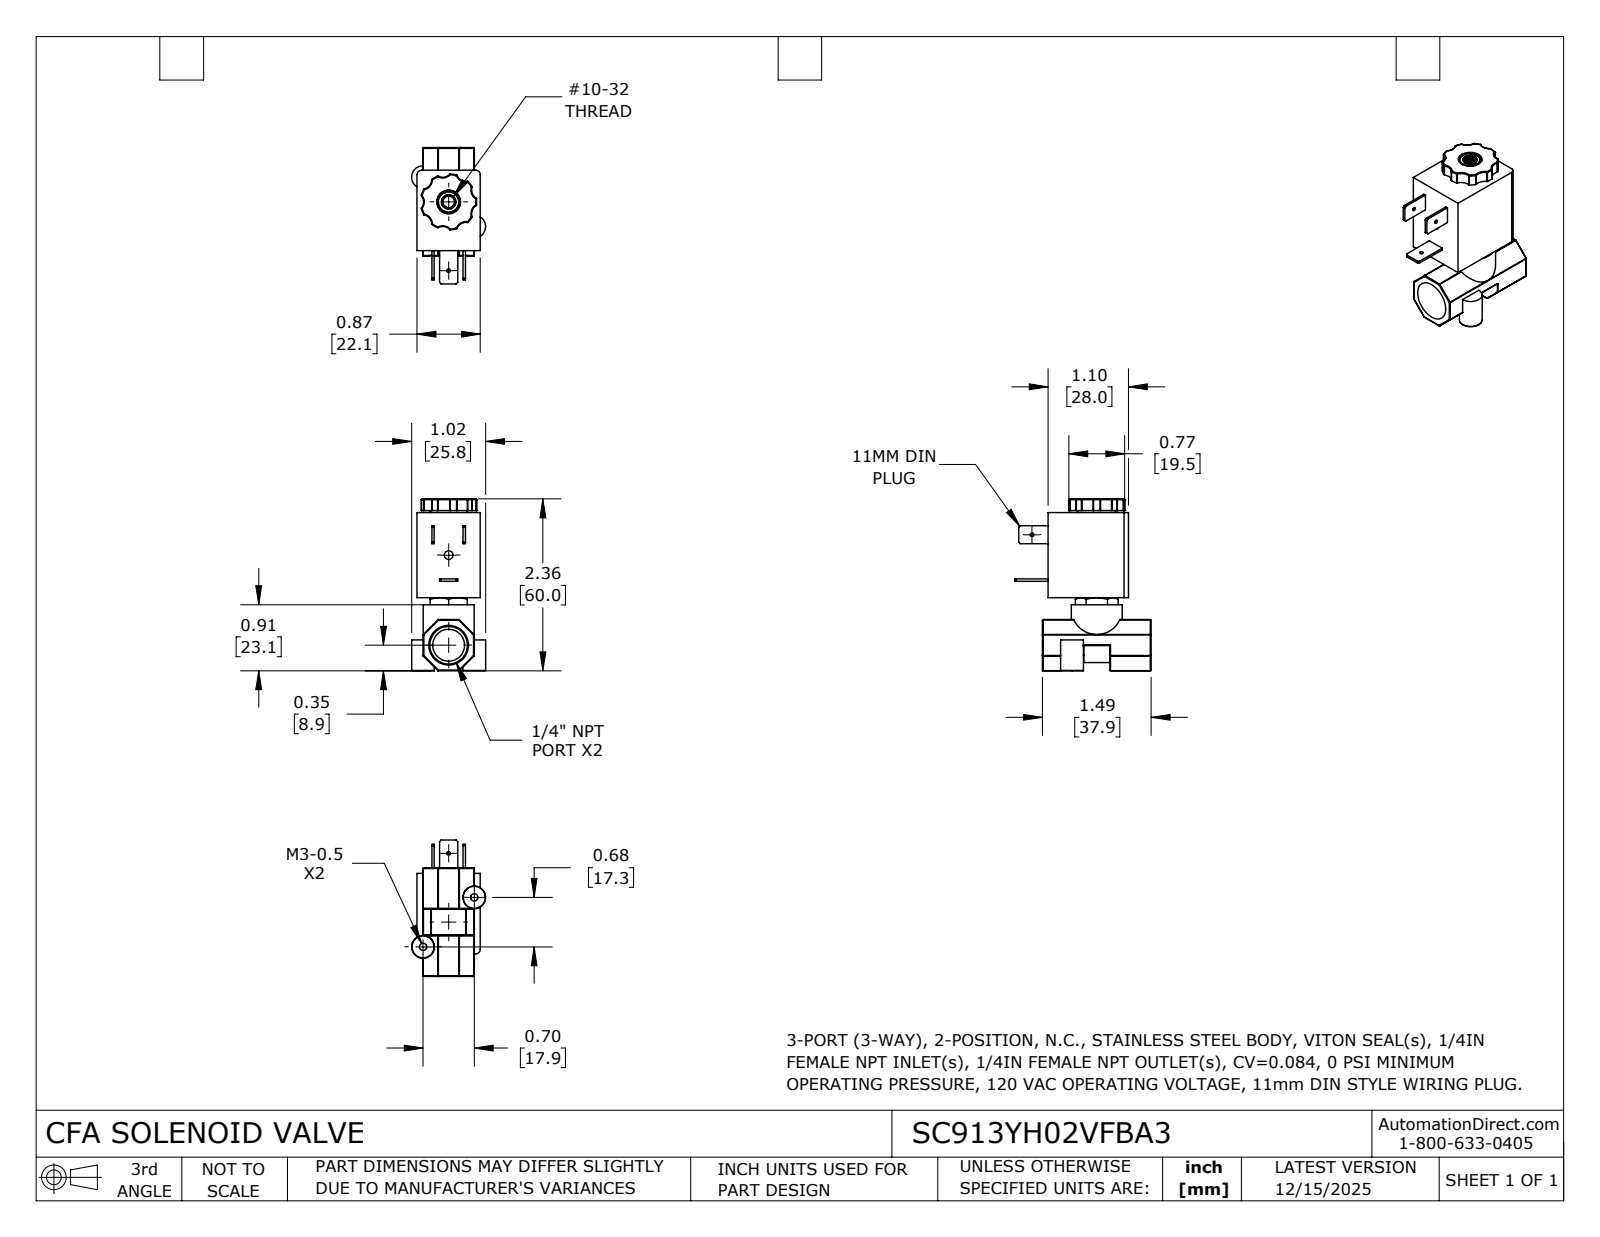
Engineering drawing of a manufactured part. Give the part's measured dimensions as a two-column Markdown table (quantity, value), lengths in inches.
| quantity | value |
| --- | --- |
| part name | SC913YH02VFBA3 |
| STEP written by | SolidWorks 2024 (CONFIG_CONTROL_DESIGN) |
| units | inches |
| bodies | 1 solid, 308 faces (68 planar, 139 cylindrical, 101 other) |
| overall size | 2.363 × 1.874 × 1.017 |
| volume | 1.665 in³ |
| surface area | 16.1 in² |
| round holes (diameter × count) | 0.05 × 2, 0.1 × 2, 0.12 × 1, 0.16 × 1, 0.327 × 1, 0.438 × 1 |
| round bosses / shafts (diameter × count) | 0.313 × 2, 0.7 × 1, 0.315 × 1 |
| partial cylindrical surfaces (radius × count) | 0.01 × 42, 0.005 × 14, 0.133 × 7, 0.06 × 2, 0.132 × 2, 0.237 × 1, 0.306 × 1, 0.385 × 1 |
| main face-to-face distances | 0.87, 0.704, 1.104, 1.167, 0.083, 0.787, 1.006, 2.173, 2.363, 1.357 |
| hole center spacings | 0.489, 0.7, 0.945, 0.979, 1.238, 1.333 |
